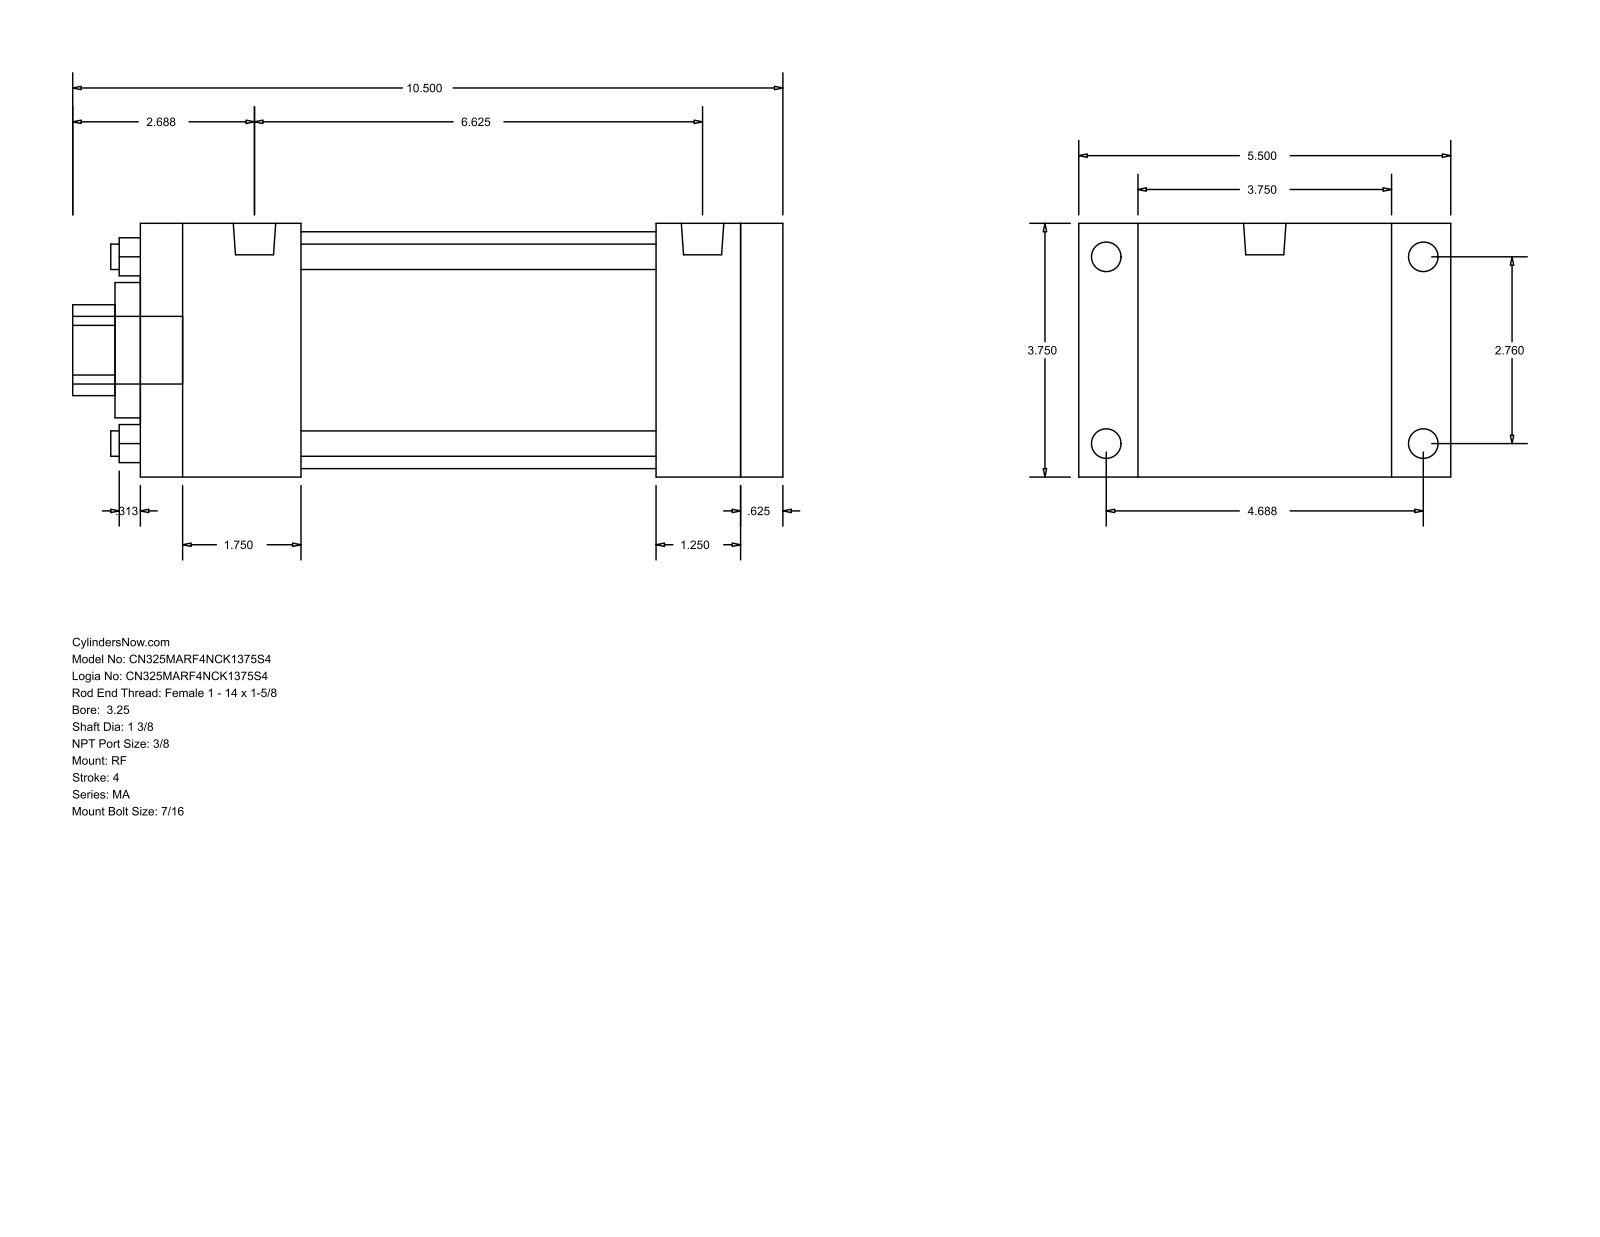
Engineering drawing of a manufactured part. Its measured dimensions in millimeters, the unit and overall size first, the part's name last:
Units: millimetres
Overall size (bounding box): 266.7 × 139.7 × 95.25
Round holes (diameter × count): ⌀9.53 ×4, ⌀34.92 ×1, ⌀50.8 ×1, ⌀88.9 ×1
Round bosses / shafts (diameter × count): ⌀11.11 ×8, ⌀15.93 ×2, ⌀25.4 ×1
Partial cylindrical surfaces — rounded edges, fillets, slot ends (radius × count): R17.06 ×1
Main face-to-face distances: 95.24, 241.3, 15.88, 225.42, 22.23, 117.47, 193.67, 31.75, 47.63, 60.32
Hole centre spacings: 49.57, 70.1, 99.14
Bodies: 0 solids, 92 faces (64 planar, 28 cylindrical, 0 other)
Part name (STEP PRODUCT): MA_RF__0325_1.375
STEP written by: GSSL Pune (CONFIG_CONTROL_DESIGN)
